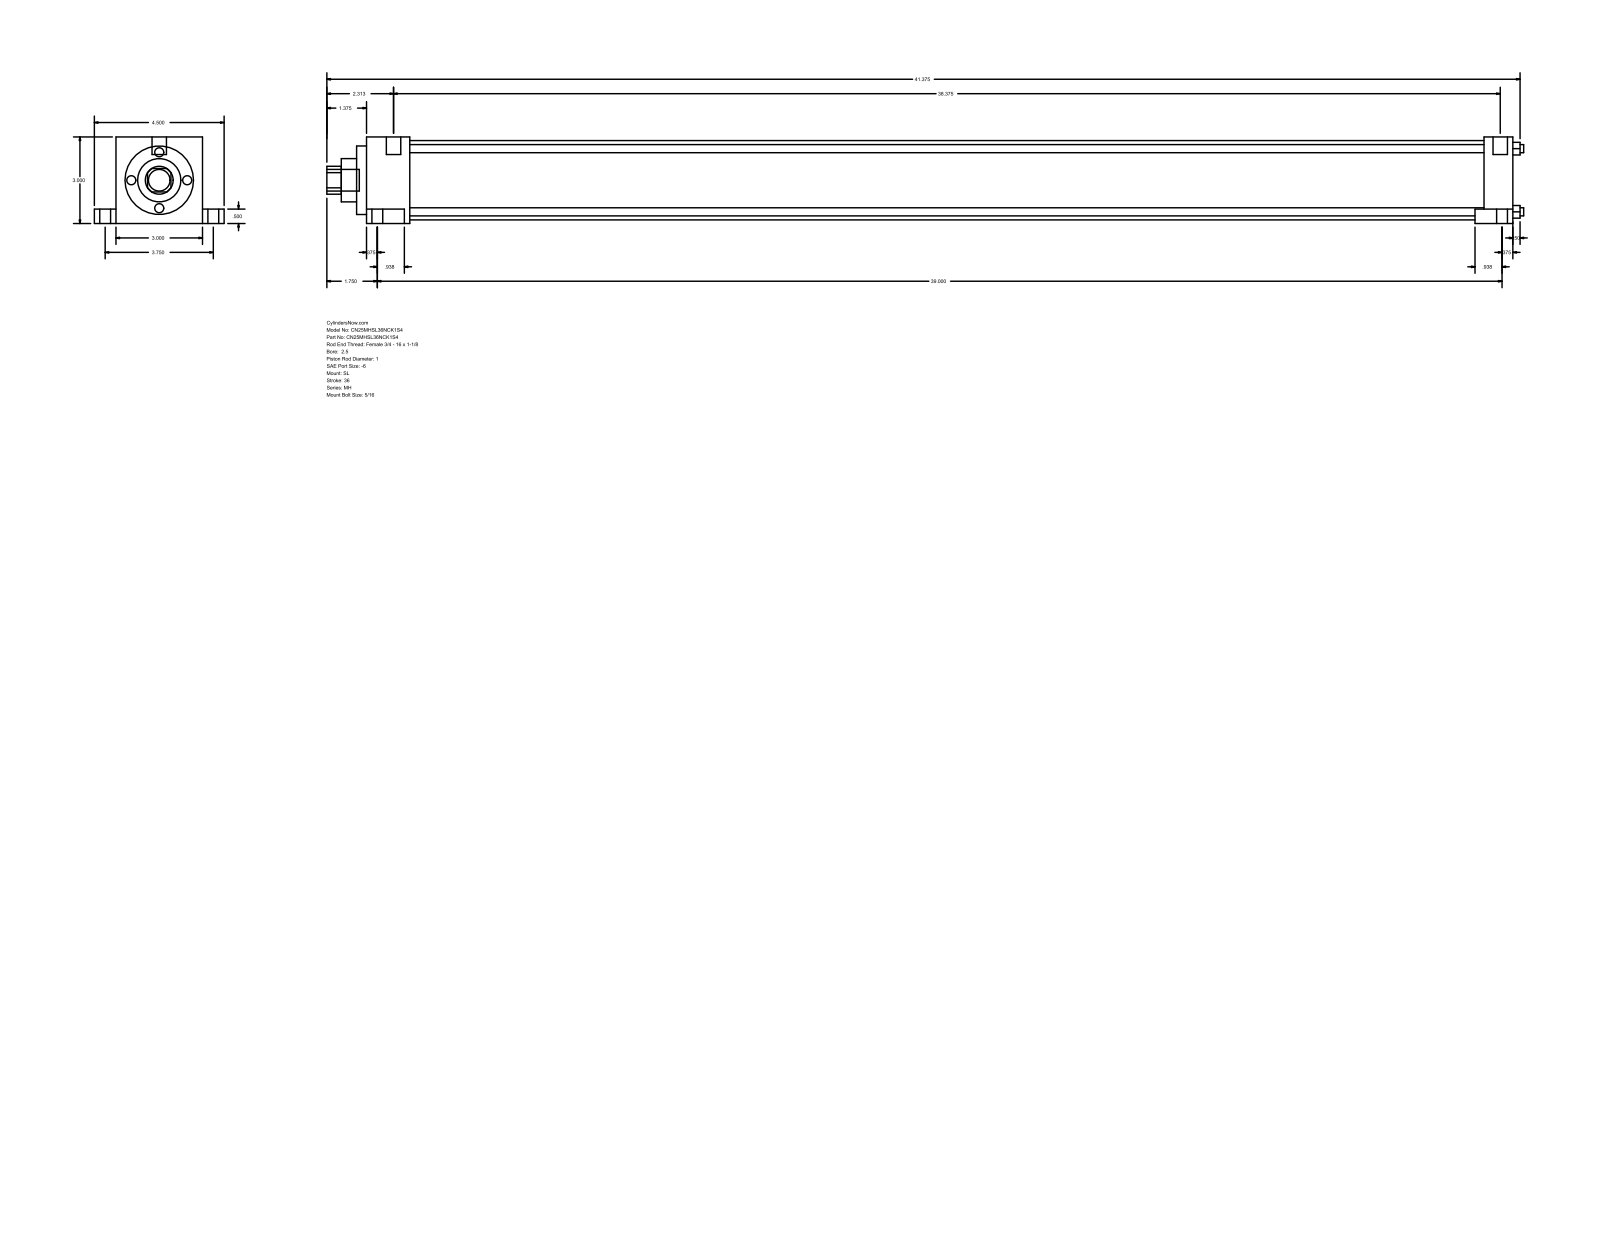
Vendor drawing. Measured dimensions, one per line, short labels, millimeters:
name: MH_SL__0250_1
written by: GSSL Pune (CONFIG_CONTROL_DESIGN)
unit: mm
bodies: 0 solids, 86 faces (61 planar, 25 cylindrical, 0 other)
size: 1054.1 × 114.3 × 76.2
holes: 4× ⌀7.14, 1× ⌀25.4, 1× ⌀38.1, 1× ⌀60.33, 1× ⌀69.85
bosses: 2× ⌀15.88, 2× ⌀9.53, 2× ⌀5.56, 1× ⌀19.05, 1× ⌀12.7
rounds: 1× R12.29
face distances: 76.2, 25.41, 992.98, 1018.39, 12.7, 63.5, 19.05, 95.25, 13.49, 1006.47
hole spacings: 39.33, 55.62, 78.66
